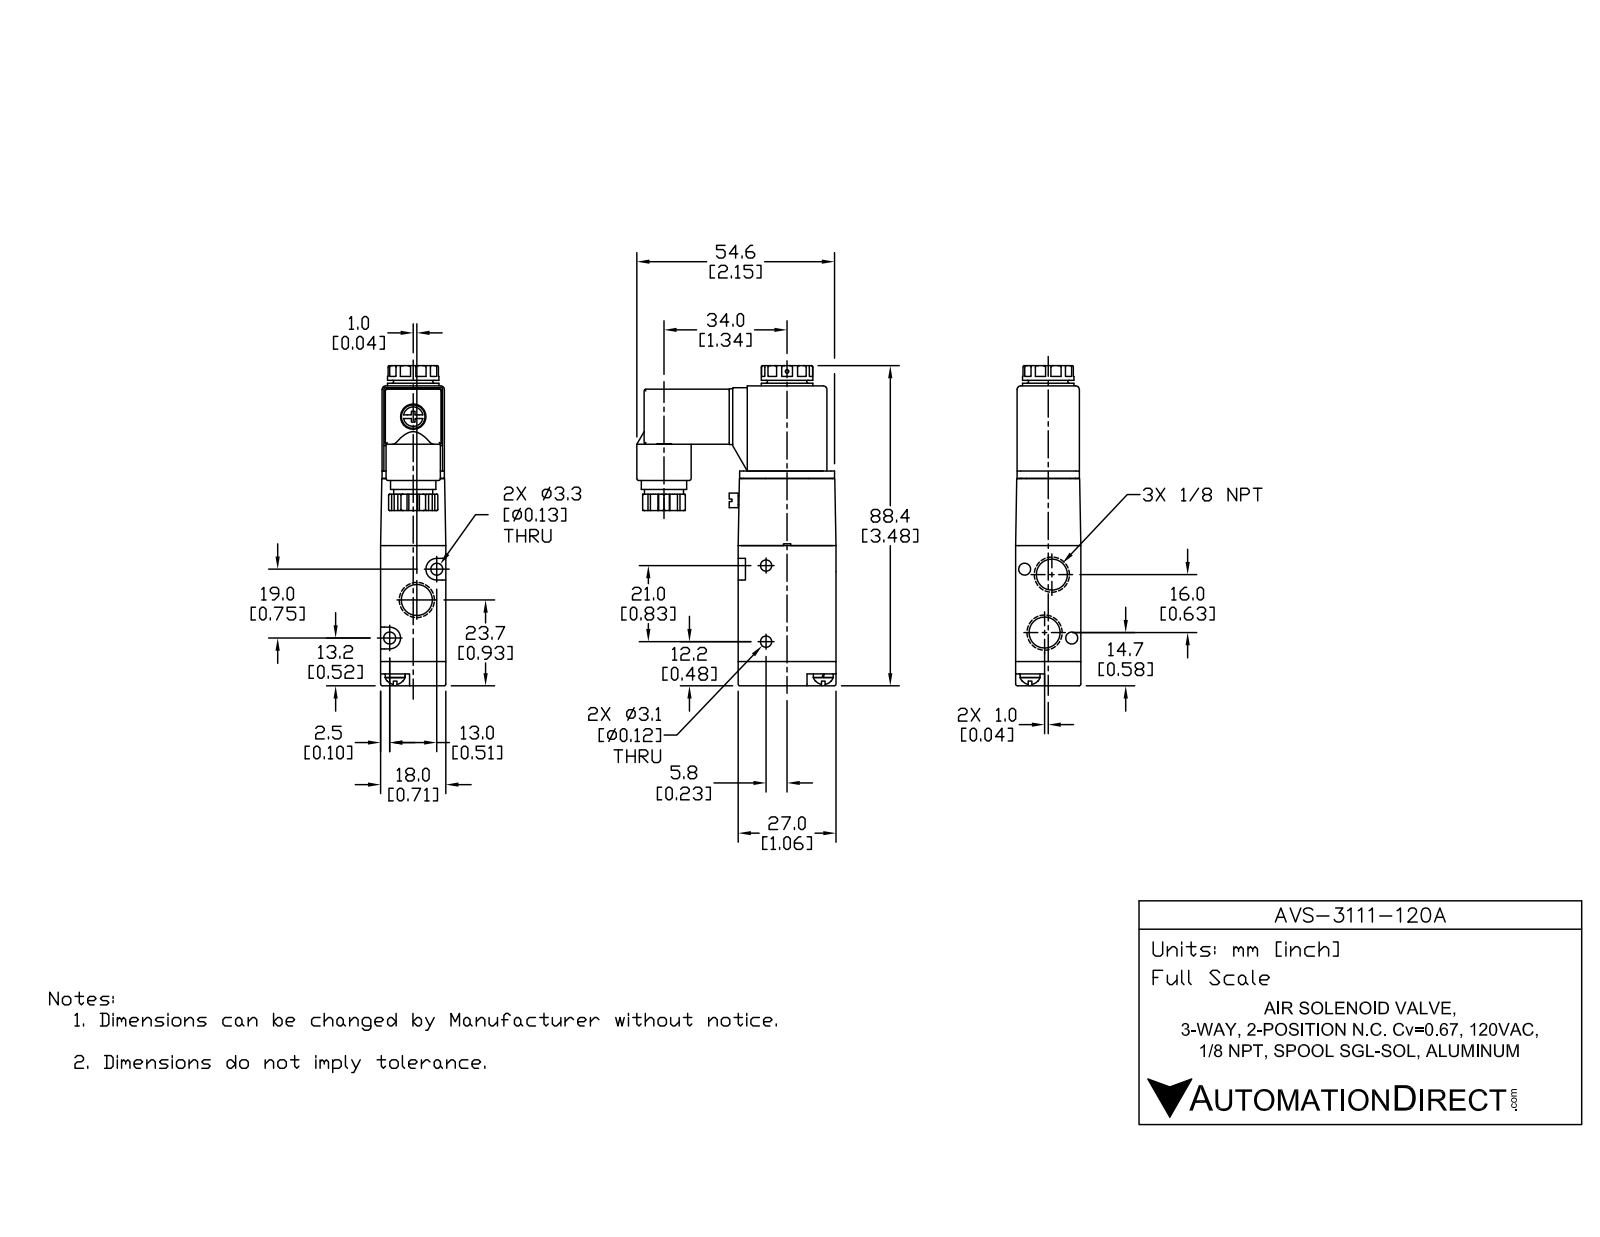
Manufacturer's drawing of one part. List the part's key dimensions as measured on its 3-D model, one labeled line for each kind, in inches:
Part name (STEP PRODUCT): AVS-3111-120A
STEP written by: SolidWorks 2015 (CONFIG_CONTROL_DESIGN)
Units: inches
Bodies: 4 solids, 137 faces (72 planar, 51 cylindrical, 14 other)
Overall size (bounding box): 3.48 × 2.165 × 0.709
Volume: 2.701 in³ · Surface area: 23.64 in²
Round holes (diameter × count): ⌀0.13 ×3, ⌀0.332 ×3, ⌀0.126 ×1, ⌀0.366 ×1
Round bosses / shafts (diameter × count): ⌀0.591 ×1, ⌀0.567 ×1, ⌀0.496 ×1, ⌀0.425 ×1, ⌀0.354 ×1, ⌀0.268 ×1
Partial cylindrical surfaces — rounded edges, fillets, slot ends (radius × count): R0.02 ×15, R0.039 ×4, R0.118 ×2
Main face-to-face distances: 1.26, 0.709, 0.657, 0.051, 0.091, 0.264, 1.524, 3.224, 2.961, 1.701
Hole centre spacings: 0.301, 0.722, 0.287, 0.354, 0.398, 0.508, 0.635, 0.827
